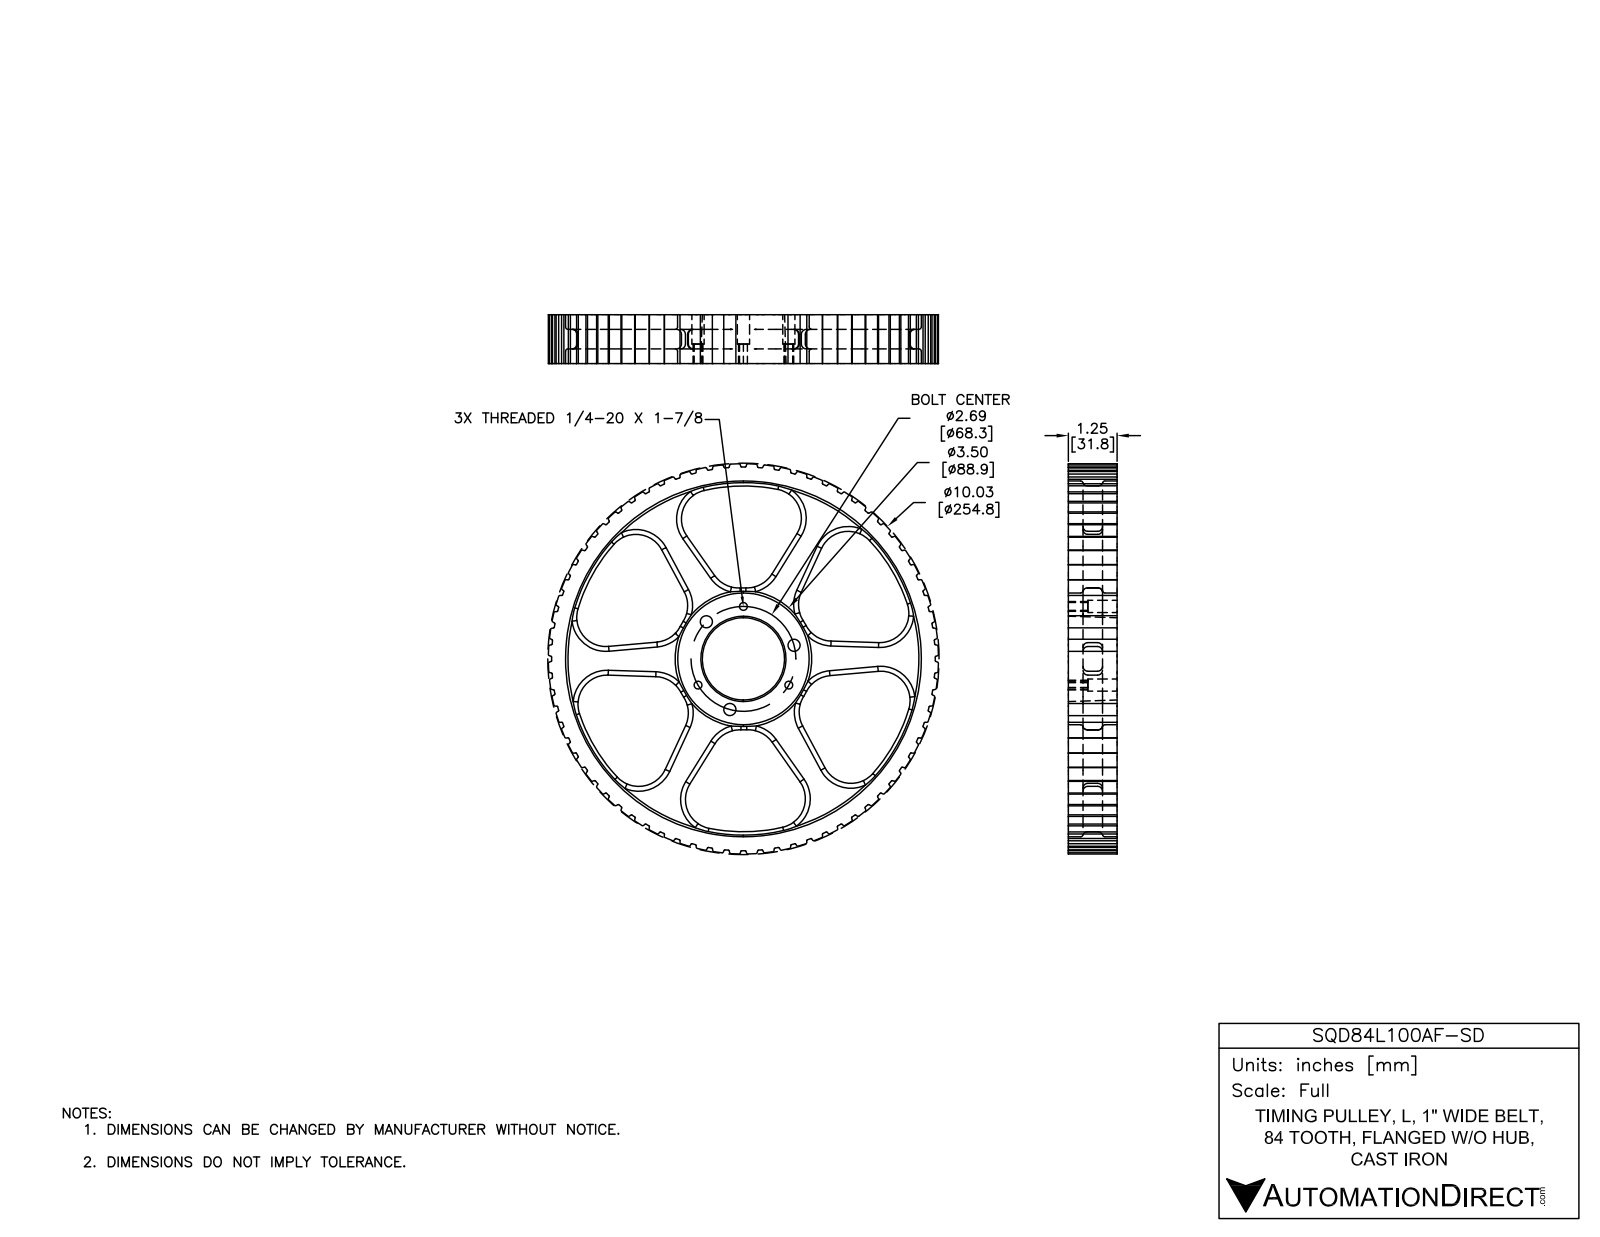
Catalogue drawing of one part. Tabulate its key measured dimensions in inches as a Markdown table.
| quantity | value |
| --- | --- |
| part name | SQD84L100AF-SD |
| STEP written by | SolidWorks 2014 (AUTOMOTIVE_DESIGN) |
| units | inches |
| bodies | 1 solid, 1004 faces (247 planar, 509 cylindrical, 248 other) |
| overall size | 9.998 × 9.998 × 1.25 |
| volume | 30.31 in³ |
| surface area | 182.1 in² |
| round holes (diameter × count) | 0.201 × 3, 0.31 × 3, 0.313 × 3, 9.12 × 1 |
| round bosses / shafts (diameter × count) | 3.375 × 1 |
| partial cylindrical surfaces (radius × count) | 0.02 × 144, 0.021 × 144, 0.125 × 36, 0.875 × 18, 1.751 × 1, 4.497 × 1, 5 × 1 |
| main face-to-face distances | 1.25, 0.312, 0.938, 0.626, 3.291, 3.25, 6.541, 6.543, 3.25, 9.833 |
| hole center spacings | 1.344, 2.327, 2.328, 2.665, 1.028, 1.636, 1.029, 1.343 |
